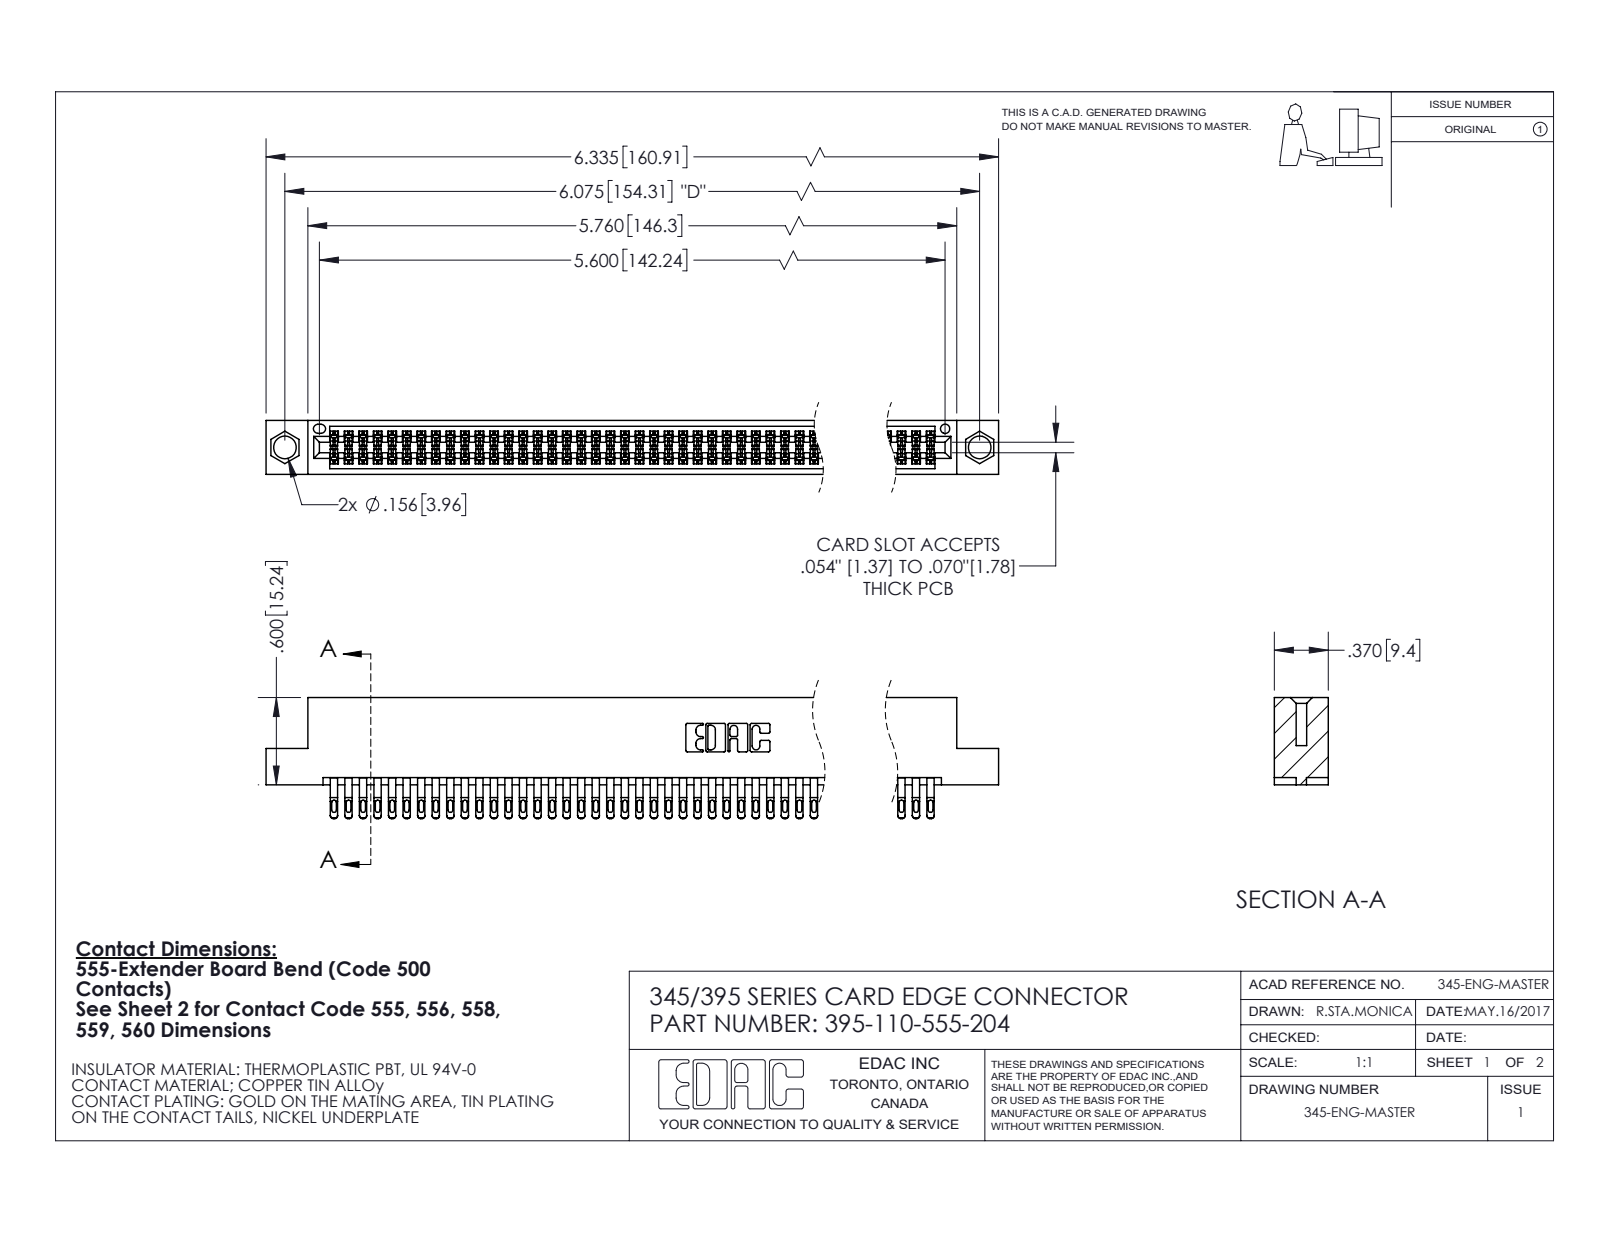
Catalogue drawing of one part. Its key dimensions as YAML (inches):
part_name: "345-292-001_555 Tail; 345 Part_Flush Mounting Lugs - 0.156 Dia-TI; 395-110-555-204"
step_written_by: "SolidWorks 2020 (CONFIG_CONTROL_DESIGN)"
units: inches
bodies: {solids: 111, faces: 6300, planar: 3504, cylindrical: 2796, other: 0}
overall_size: [6.335, 0.832, 0.37]
volume: 0.974
surface_area: 38.46
round_holes:
  - {diameter: 0.156, count: 2}
  - {diameter: 0.064, count: 1}
partial_cylinders:
  - {radius: 0.016, count: 275}
  - {radius: 0.006, count: 220}
  - {radius: 0.02, count: 220}
  - {radius: 0.01, count: 22}
  - {radius: 0.007, count: 6}
  - {radius: 0.031, count: 6}
  - {radius: 0.026, count: 3}
  - {radius: 0.01, count: 2}
face_to_face_distances: [0.298, 0.072, 0.025, 0.37, 0.2, 0.098, 0.272, 0.225, 0.175, 0.149]
hole_center_spacings: [0.27, 5.839, 6.075]
